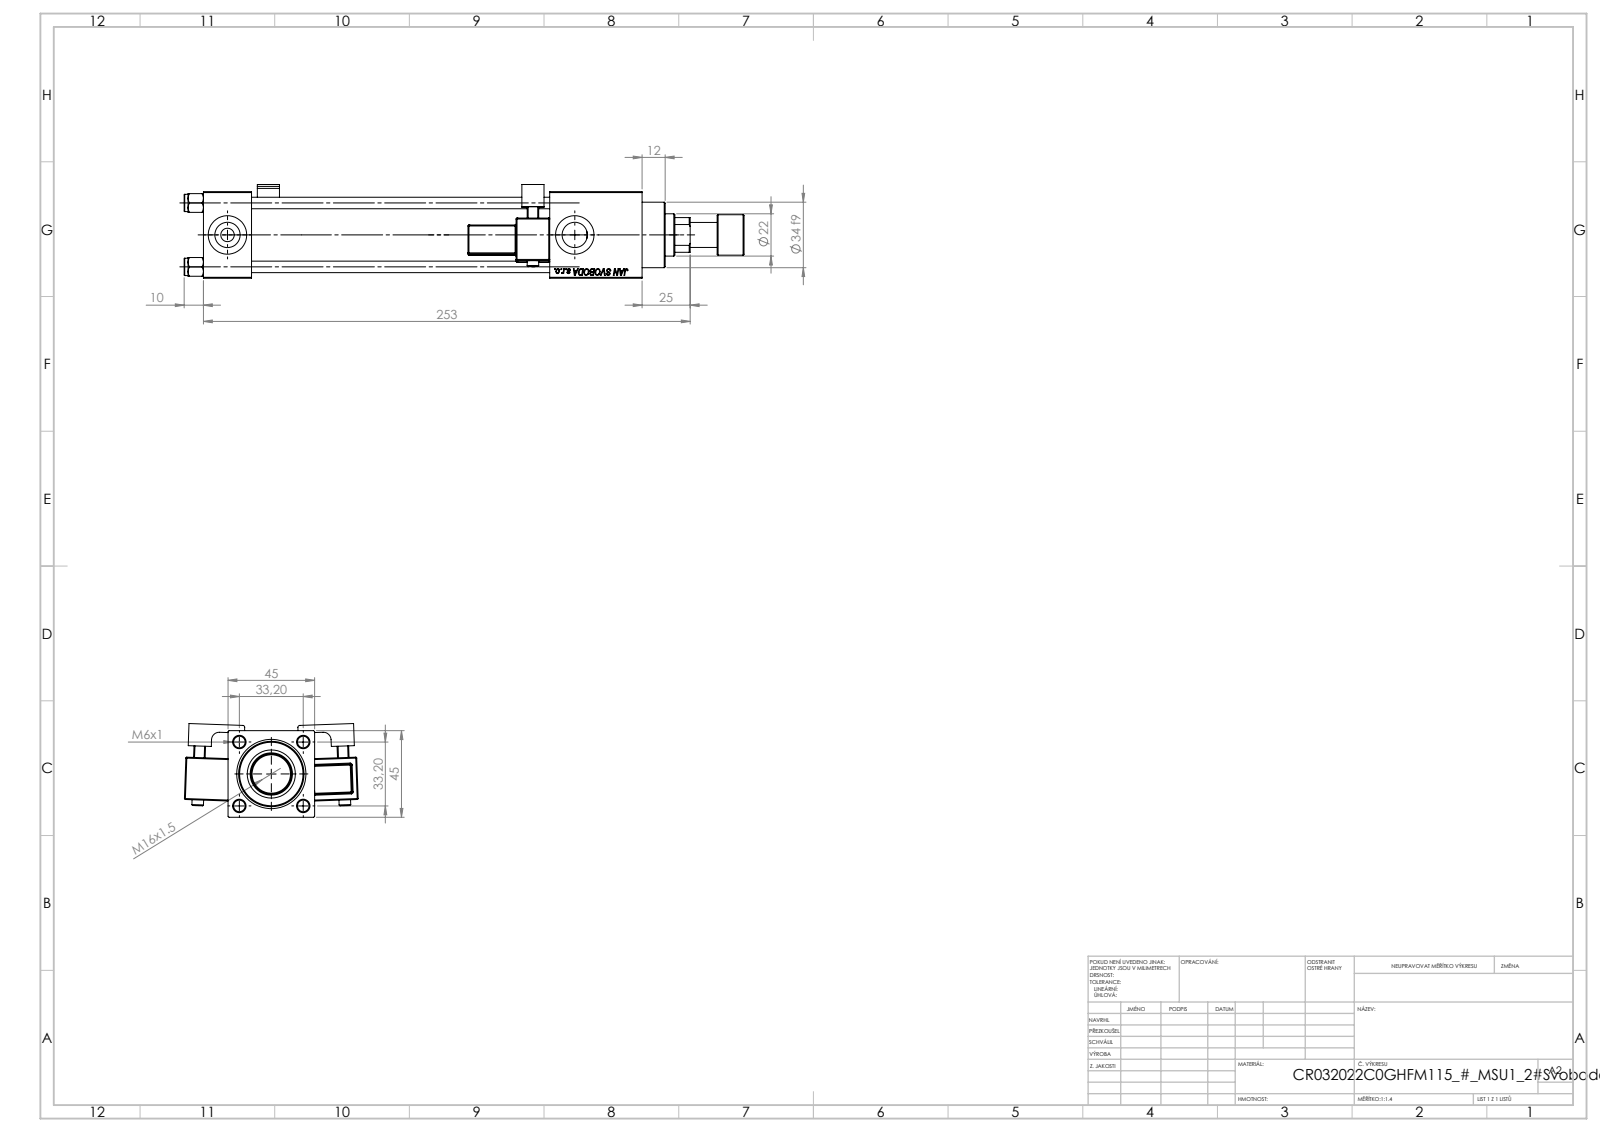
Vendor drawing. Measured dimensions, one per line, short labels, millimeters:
name: V215CR_C_Body; V215CR_VCP_C; V215CR_C_TYCINKA; NUT_M5_C (+3 more)
written by: SolidWorks 2019 (CONFIG_CONTROL_DESIGN)
unit: mm
bodies: 14 solids, 1316 faces (590 planar, 150 cylindrical, 576 other)
size: 291 × 90.31 × 48.72
volume: 343 643 mm³; area: 123 727 mm²
holes: 4× ⌀6, 2× ⌀7, 2× ⌀13.16, 2× ⌀20, 1× ⌀10.5, 1× ⌀22, 1× ⌀24, 1× ⌀25, 1× ⌀32, 1× ⌀33
bosses: 4× ⌀9, 2× ⌀6, 1× ⌀38, 1× ⌀34, 1× ⌀21, 1× ⌀13
rounds: 48× R0.5, 2× R1, 2× R2.5, 2× R4
face distances: 45, 25, 3, 180, 155, 22.99, 228, 137.5, 203, 28
hole spacings: 23.48, 33.2, 46.95, 180.5
